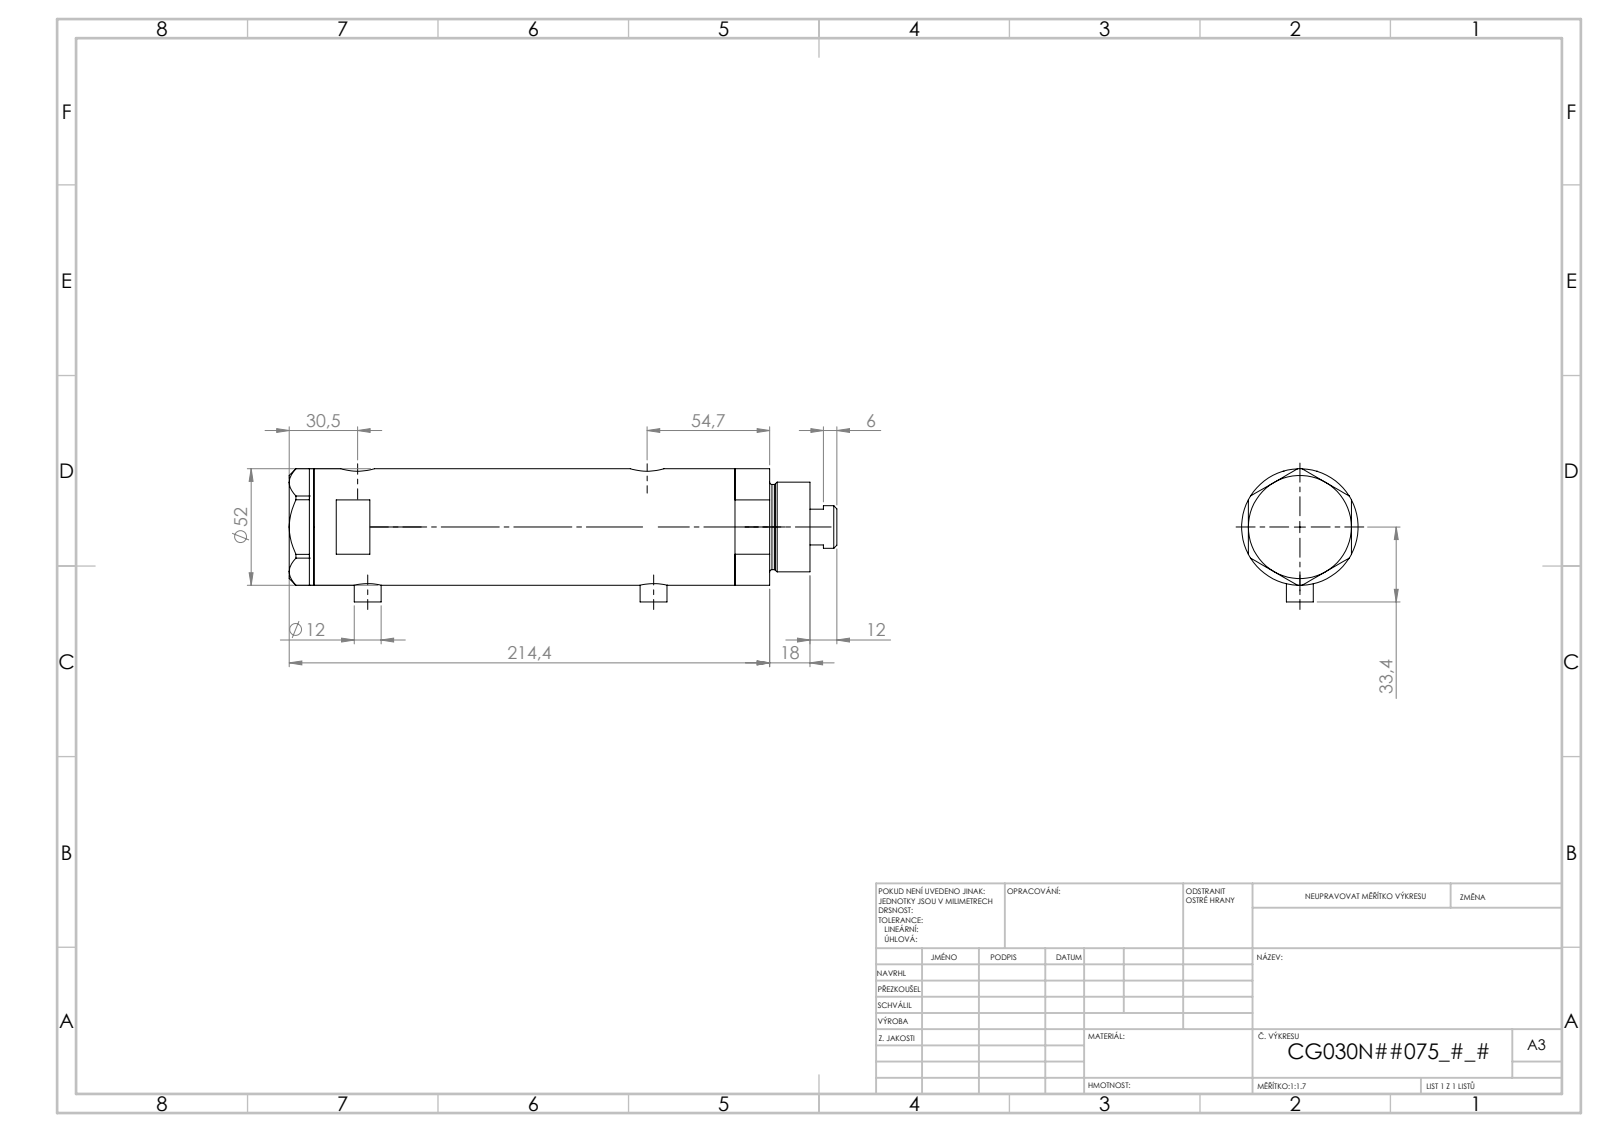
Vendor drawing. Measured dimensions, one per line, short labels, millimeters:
name: V270CG_VC; V270CG_BACK; V270CG_FRONT; V270CG_MIDDLE
written by: SolidWorks 2019 (CONFIG_CONTROL_DESIGN)
unit: mm
bodies: 4 solids, 140 faces (67 planar, 53 cylindrical, 20 other)
size: 224.02 × 53.1 × 52
volume: 397 345 mm³; area: 89 123 mm²
holes: 2× ⌀5, 2× ⌀9.73, 2× ⌀12.5, 2× ⌀15, 1× ⌀6.5, 1× ⌀20, 1× ⌀21.5, 1× ⌀30, 1× ⌀33, 1× ⌀44
bosses: 2× ⌀12, 1× ⌀52, 1× ⌀40, 1× ⌀38, 1× ⌀19
face distances: 128.54, 23.8, 104.74, 11, 34.8, 139.54, 46, 175.94, 164.94, 141.14
hole spacings: 2.9, 4.5, 101.75, 104.65, 106.25, 109.15, 2.89, 2.91
